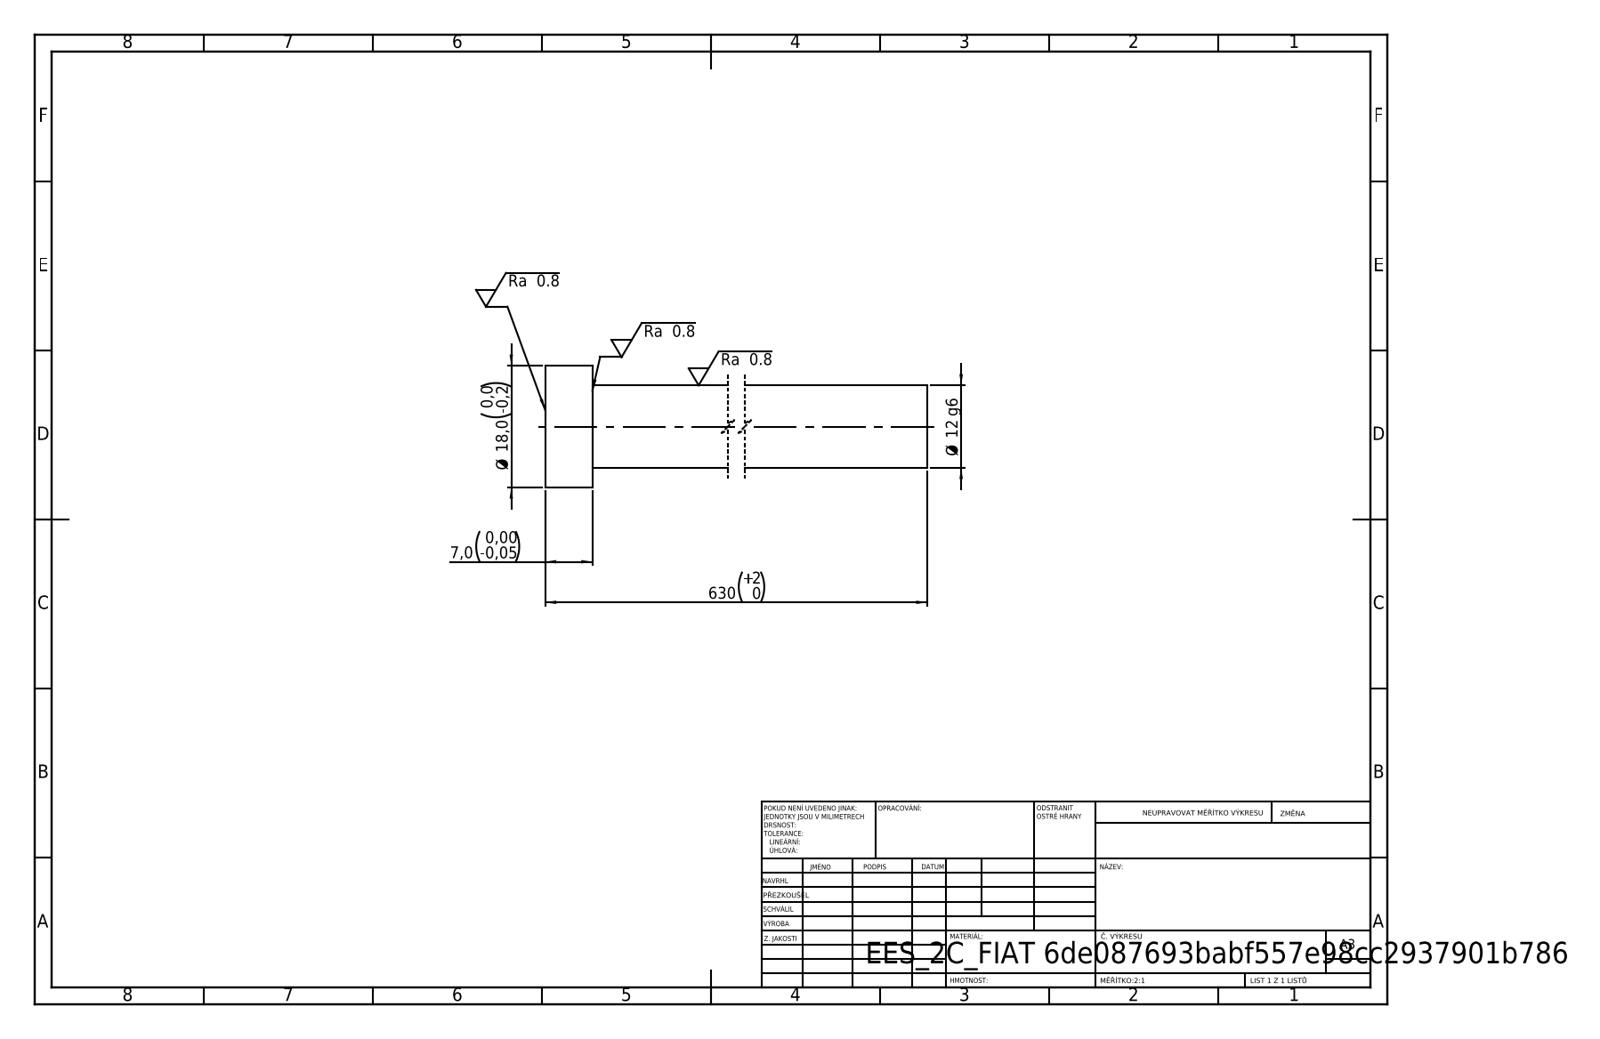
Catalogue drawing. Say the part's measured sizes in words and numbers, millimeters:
Its 3-D file was written by "SolidWorks 2019 (CONFIG_CONTROL_DESIGN)". It is 1 solid with 7 faces: 3 planar, 4 cylindrical and 0 other. Overall it measures 630 by 18 by 18 millimeters. Its volume is 74 609 cubic millimeters and its surface area 24 783 square millimeters. Round bosses or shafts: 1 of diameter 18, 1 of diameter 12.2. The main face-to-face distances are 7, 630, 623.
